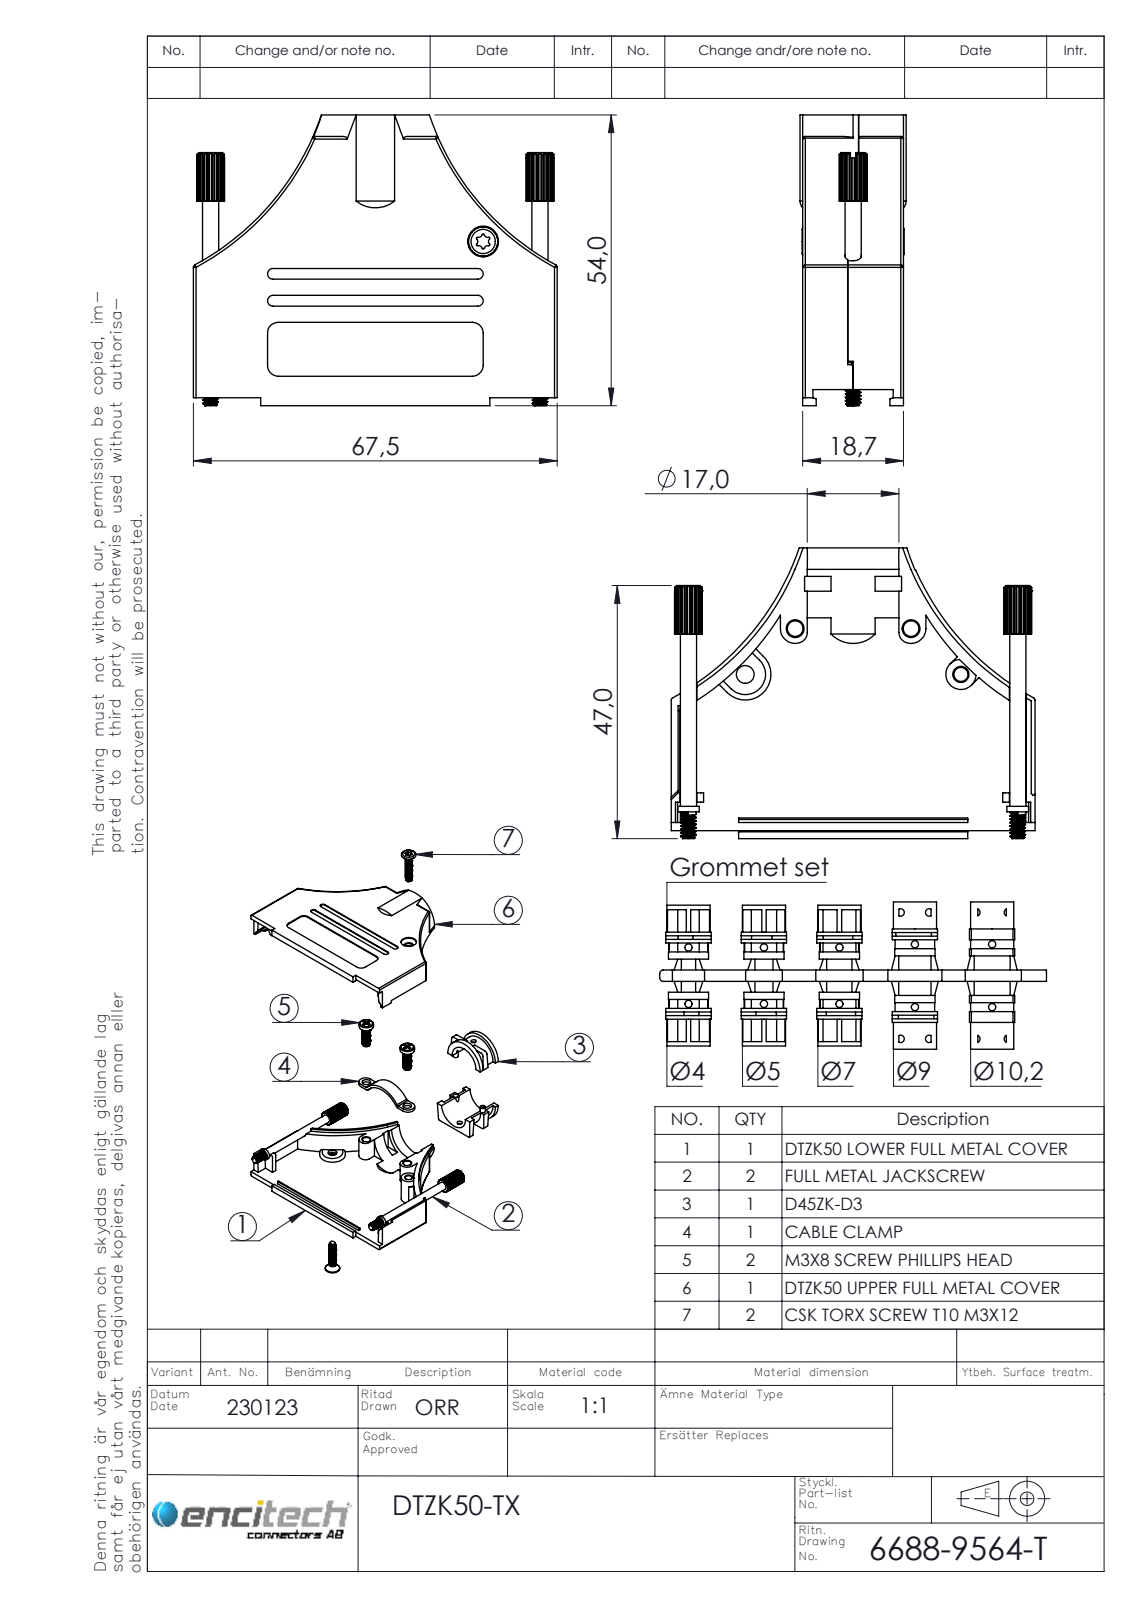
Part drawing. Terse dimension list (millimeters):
name: 6805-0105-15; 6826-0141-02; 6522-0121-06 (12.5 mm SV); 6830-0109-04 (+5 more)
written by: SolidWorks 2021 (AUTOMOTIVE_DESIGN)
unit: mm
bodies: 11 solids, 891 faces (339 planar, 398 cylindrical, 154 other)
size: 67.5 × 54 × 19.7
volume: 17 721 mm³; area: 21 062 mm²
holes: 4× ⌀2, 2× ⌀2.6, 2× ⌀2.9, 2× ⌀3.1, 2× ⌀3.2, 2× ⌀3.3, 2× ⌀3.31, 2× ⌀5.7, 1× ⌀12.5
bosses: 4× ⌀3, 2× ⌀4, 2× ⌀2.85, 2× ⌀2.5, 2× ⌀1.9, 1× ⌀17, 1× ⌀14.5
rounds: 22× R0.5, 22× R1, 12× R0.18, 12× R0.7, 6× R2, 6× R50, 4× R0.25, 2× R0.3
face distances: 1.9, 16.8, 14.9, 18.7, 18.4, 1.6, 16.5, 7.45, 9.35, 9.05
hole spacings: 7.45, 8.66, 9.02, 11.25, 12.56, 15.03, 19.66, 21.14
